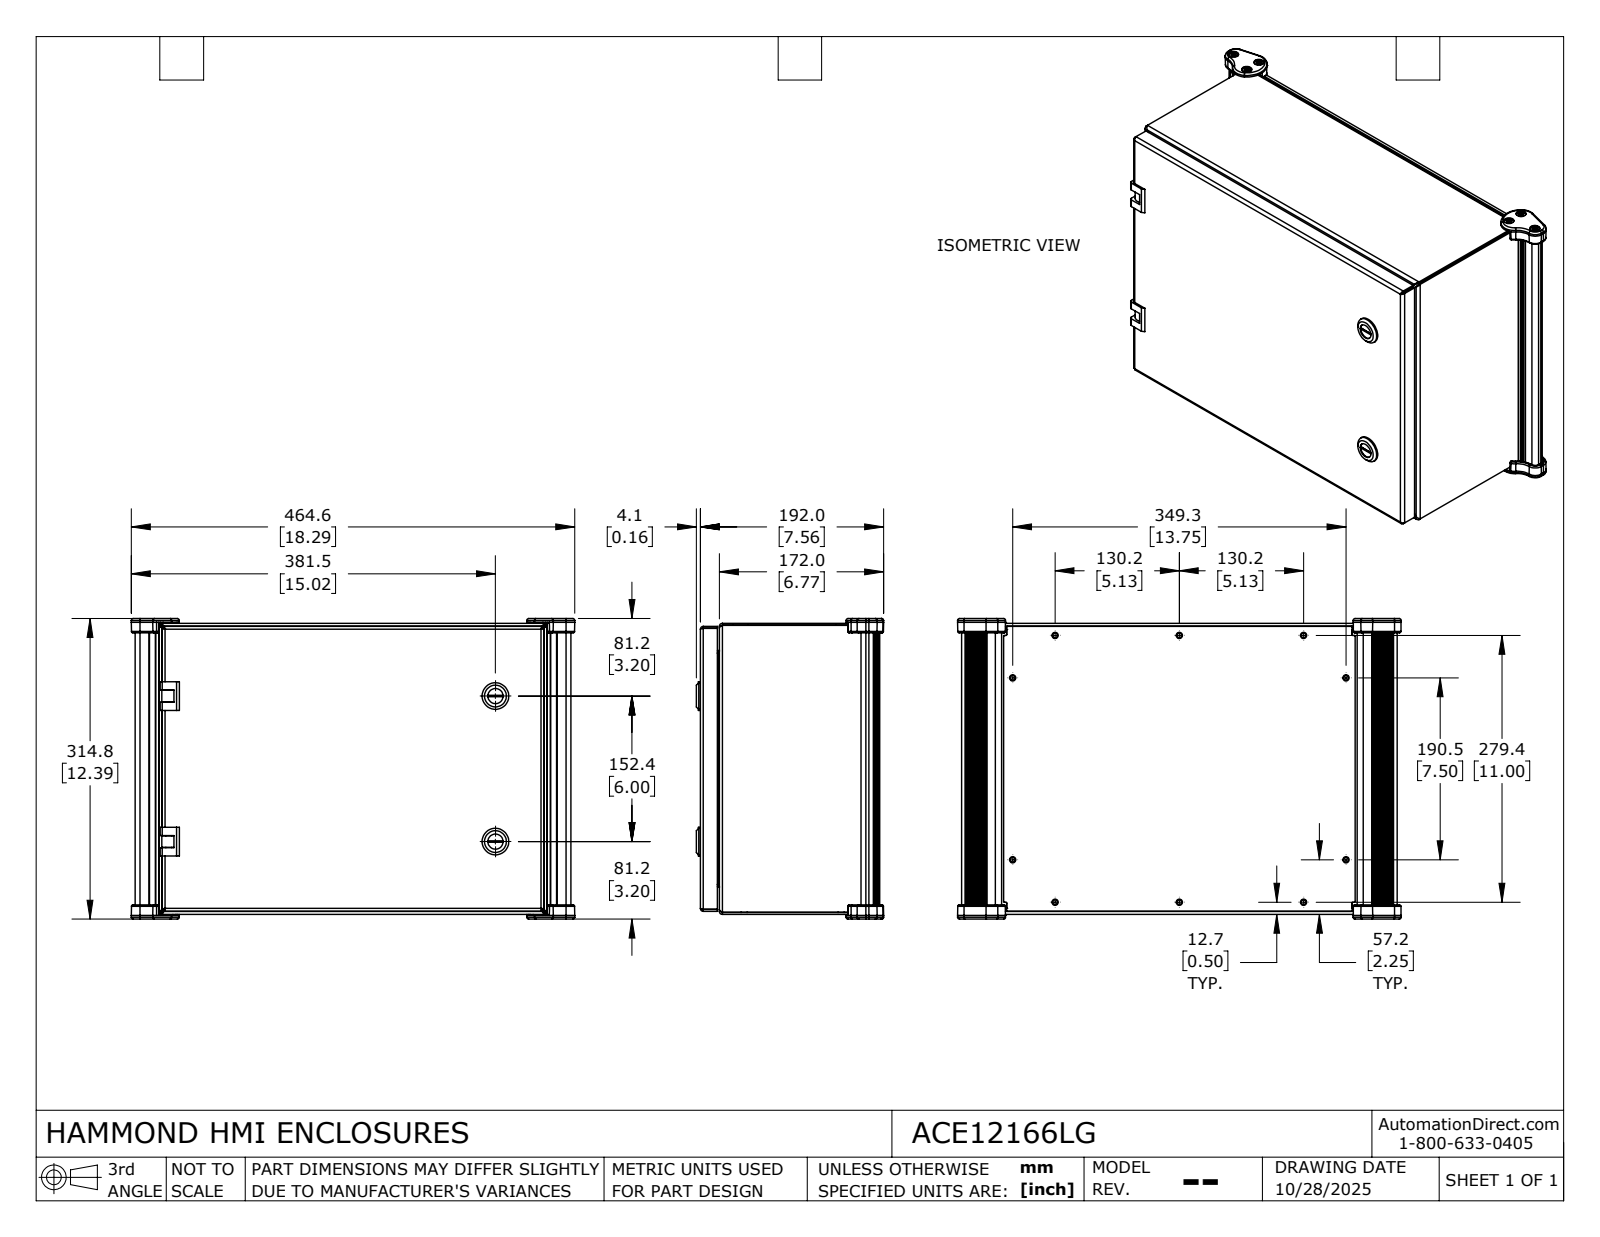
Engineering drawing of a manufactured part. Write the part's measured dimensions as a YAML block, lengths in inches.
part_name: "ACE12166LG"
step_written_by: "SolidWorks 2024 (AUTOMOTIVE_DESIGN)"
units: inches
bodies: {solids: 95, faces: 2508, planar: 1188, cylindrical: 855, other: 465}
overall_size: [18.292, 12.395, 7.719]
volume: 106.7
surface_area: 2395
round_holes:
  - {diameter: 0.156, count: 12}
  - {diameter: 0.234, count: 12}
  - {diameter: 0.19, count: 10}
  - {diameter: 0.205, count: 6}
  - {diameter: 0.413, count: 6}
  - {diameter: 0.196, count: 5}
  - {diameter: 0.159, count: 4}
  - {diameter: 0.406, count: 4}
  - {diameter: 0.16, count: 2}
  - {diameter: 0.197, count: 2}
  - {diameter: 0.232, count: 2}
  - {diameter: 0.25, count: 2}
round_bosses_or_shafts:
  - {diameter: 0.256, count: 10}
  - {diameter: 0.25, count: 6}
  - {diameter: 0.19, count: 6}
  - {diameter: 0.149, count: 6}
  - {diameter: 0.236, count: 5}
  - {diameter: 0.375, count: 4}
  - {diameter: 0.33, count: 4}
  - {diameter: 1.1, count: 2}
partial_cylinders:
  - {radius: 0.01, count: 38}
  - {radius: 0.059, count: 30}
  - {radius: 0.041, count: 20}
  - {radius: 0.122, count: 20}
  - {radius: 0.016, count: 16}
  - {radius: 0.03, count: 16}
  - {radius: 0.05, count: 16}
  - {radius: 0.039, count: 14}
face_to_face_distances: [0.081, 0.125, 6.831, 6.912, 6.956, 7.037, 0.081, 0.206, 15.919, 6.706]
hole_center_spacings: [4, 6, 2.474, 5.125, 6.786, 6.98, 7.094, 8.846]
